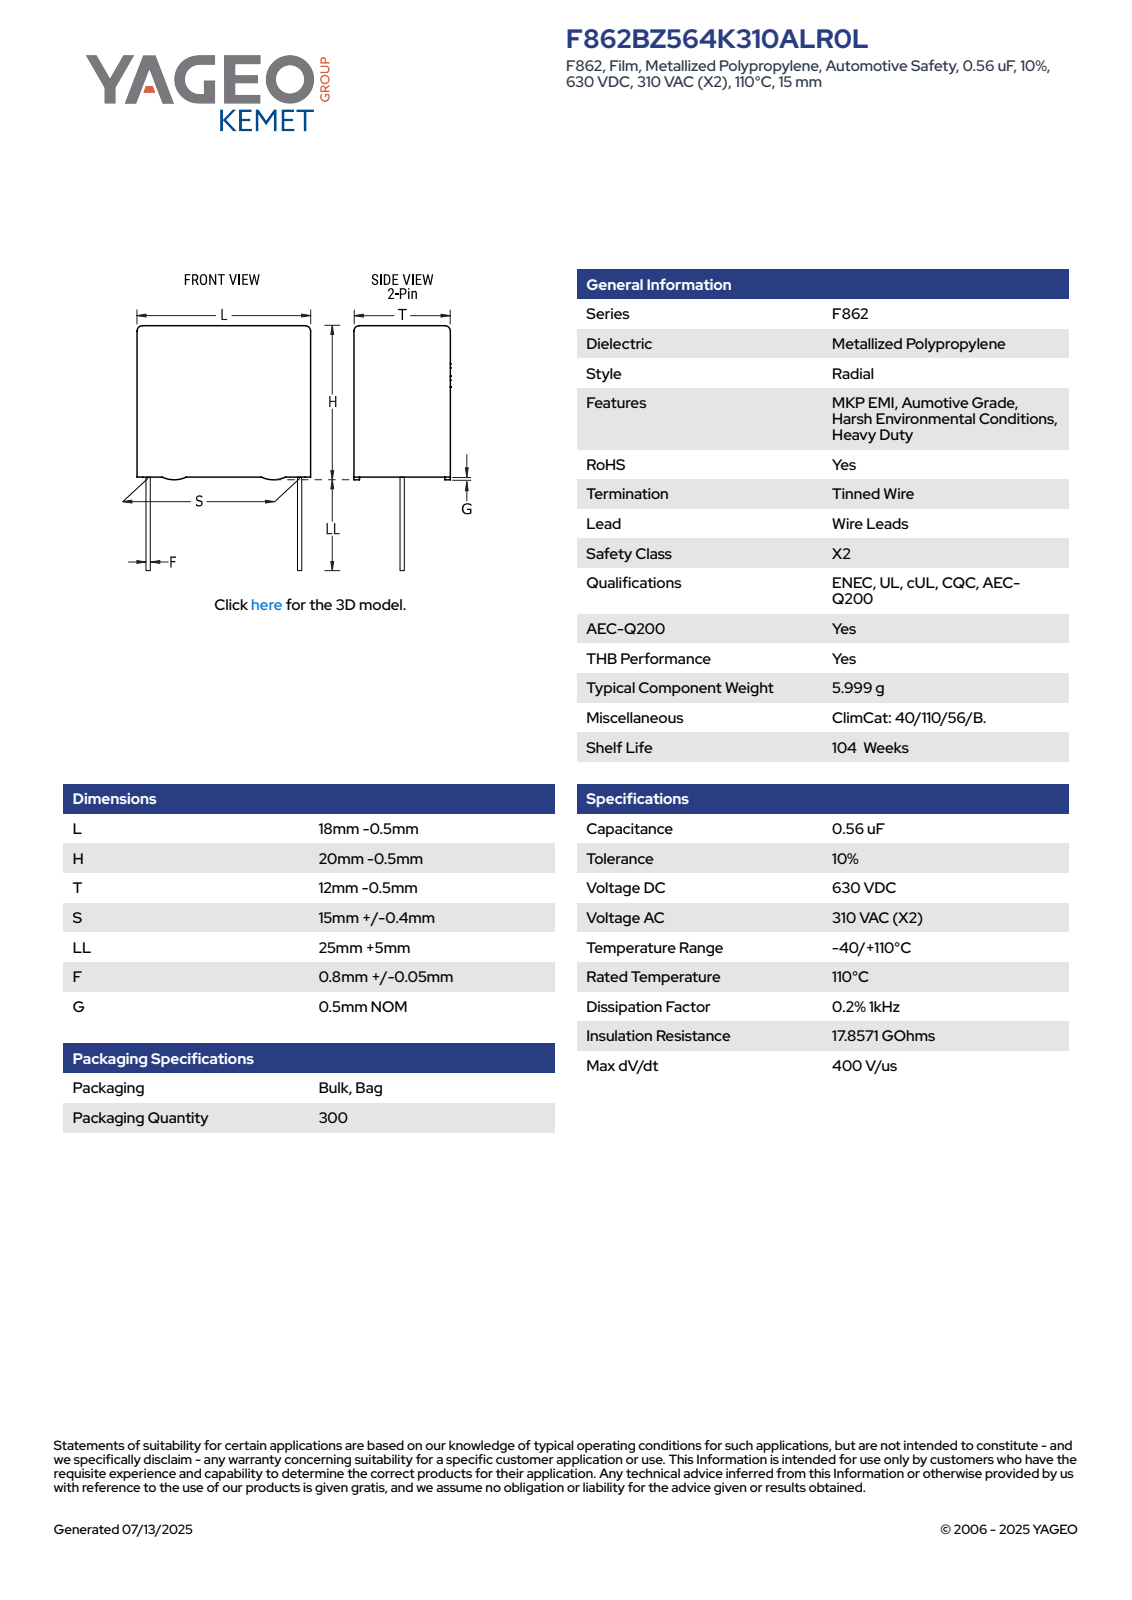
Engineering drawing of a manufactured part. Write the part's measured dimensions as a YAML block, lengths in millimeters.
part_name: "CFR_RBG_18X20X12_L17.5H19.5T11.5S15LL30F0.85G0.5"
step_written_by: "SolidWorks 2014 (AUTOMOTIVE_DESIGN)"
units: millimeters
bodies: {solids: 4, faces: 89, planar: 81, cylindrical: 8, other: 0}
overall_size: [49.5, 17.5, 11.51]
volume: 3859
surface_area: 1701
round_bosses_or_shafts:
  - {diameter: 0.85, count: 2}
partial_cylinders:
  - {radius: 0.5, count: 4}
face_to_face_distances: [11.5, 17.5, 19, 0.5, 19.5, 0.66, 10.84, 10.18, 30, 30.5]
